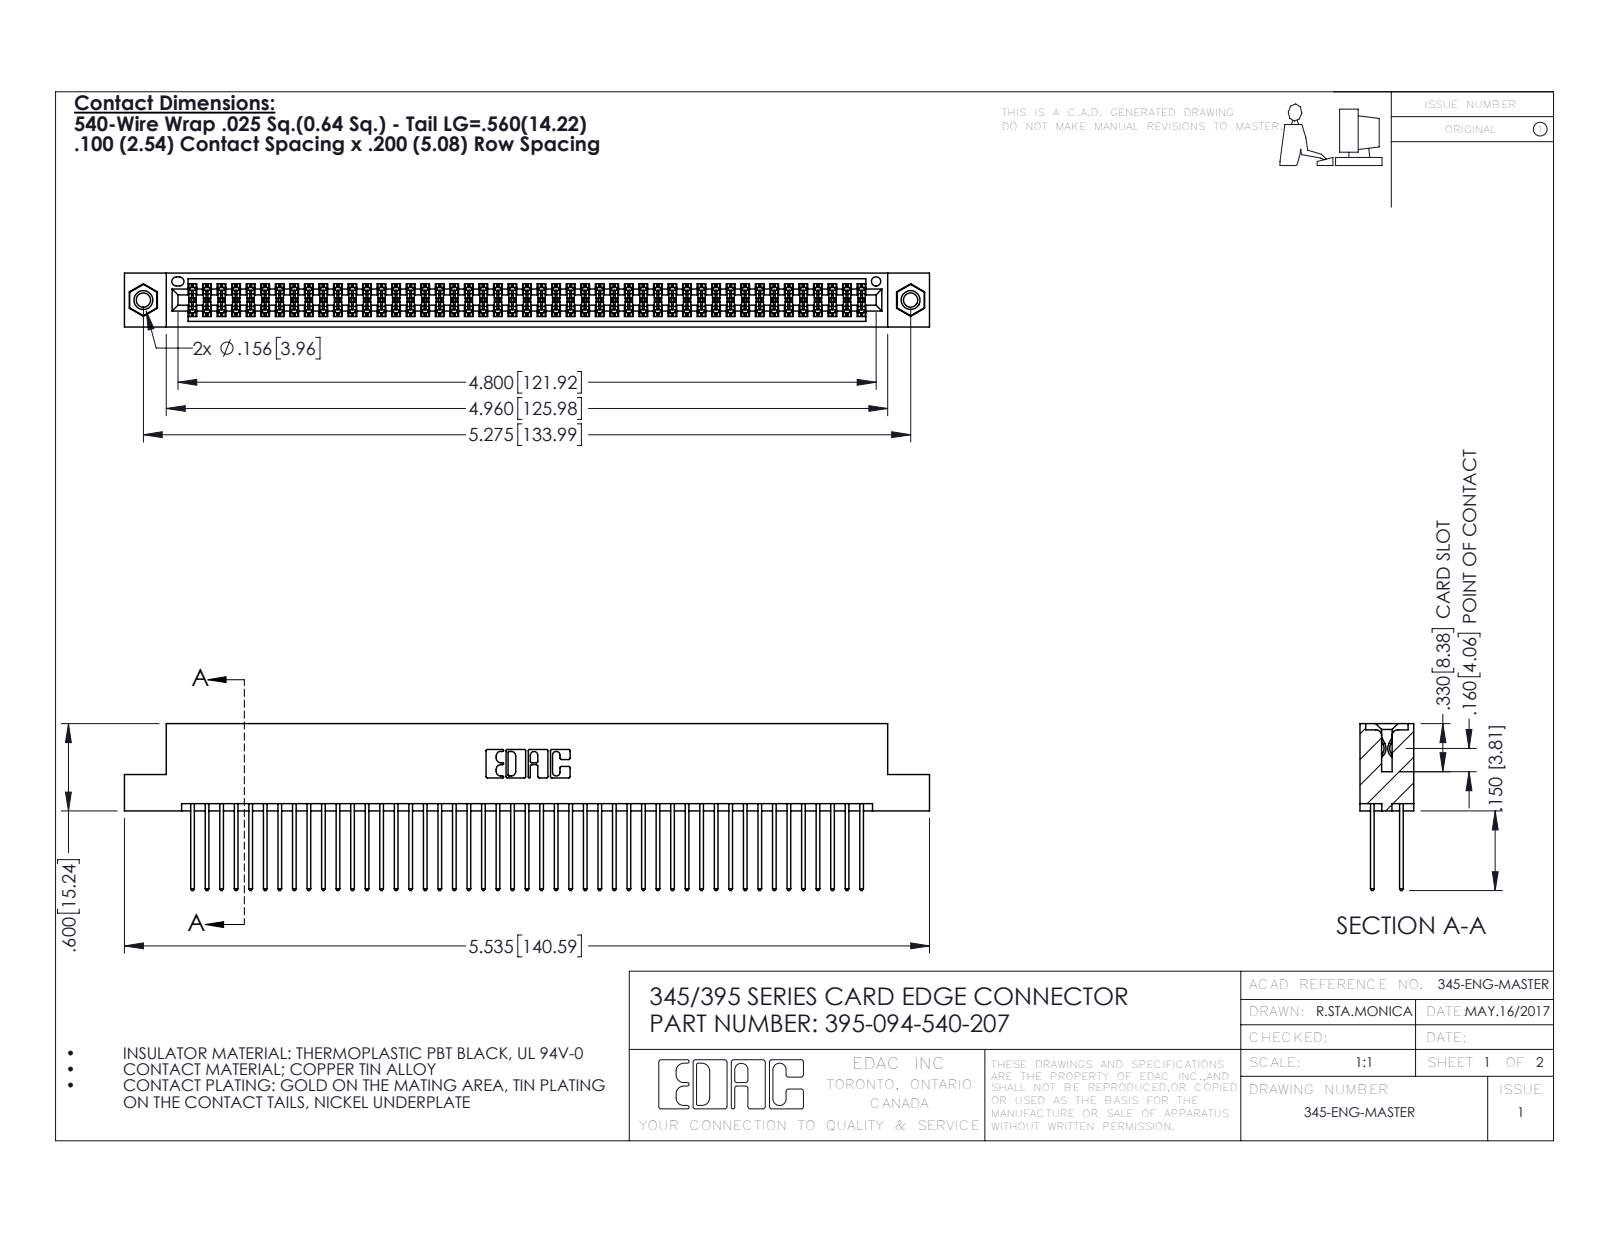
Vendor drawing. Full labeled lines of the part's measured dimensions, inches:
Part name (STEP PRODUCT): 345-250-001_345-250-005-103; 345 Part_Flush Mounting Lugs - 0.156 Dia-TI; 345-292-001_345-293-140; 395-094-540-207
STEP written by: SolidWorks 2016 (CONFIG_CONTROL_DESIGN)
Units: inches
Bodies: 97 solids, 4886 faces (3214 planar, 1656 cylindrical, 16 other)
Overall size (bounding box): 5.535 × 1.147 × 0.37
Volume: 0.857 in³ · Surface area: 34.94 in²
Round holes (diameter × count): ⌀0.098 ×2, ⌀0.125 ×2, ⌀0.156 ×2, ⌀0.064 ×1
Round bosses / shafts (diameter × count): ⌀0.155 ×2
Partial cylindrical surfaces — rounded edges, fillets, slot ends (radius × count): R0.006 ×141, R0.01 ×94, R0.01 ×22, R0.007 ×6, R0.031 ×6, R0.026 ×3, R0.014 ×2, R0.019 ×2
Main face-to-face distances: 0.072, 0.298, 0.2, 0.098, 0.272, 0.025, 0.37, 0.225, 0.175, 0.149
Hole centre spacings: 0.27, 5.039, 5.275
